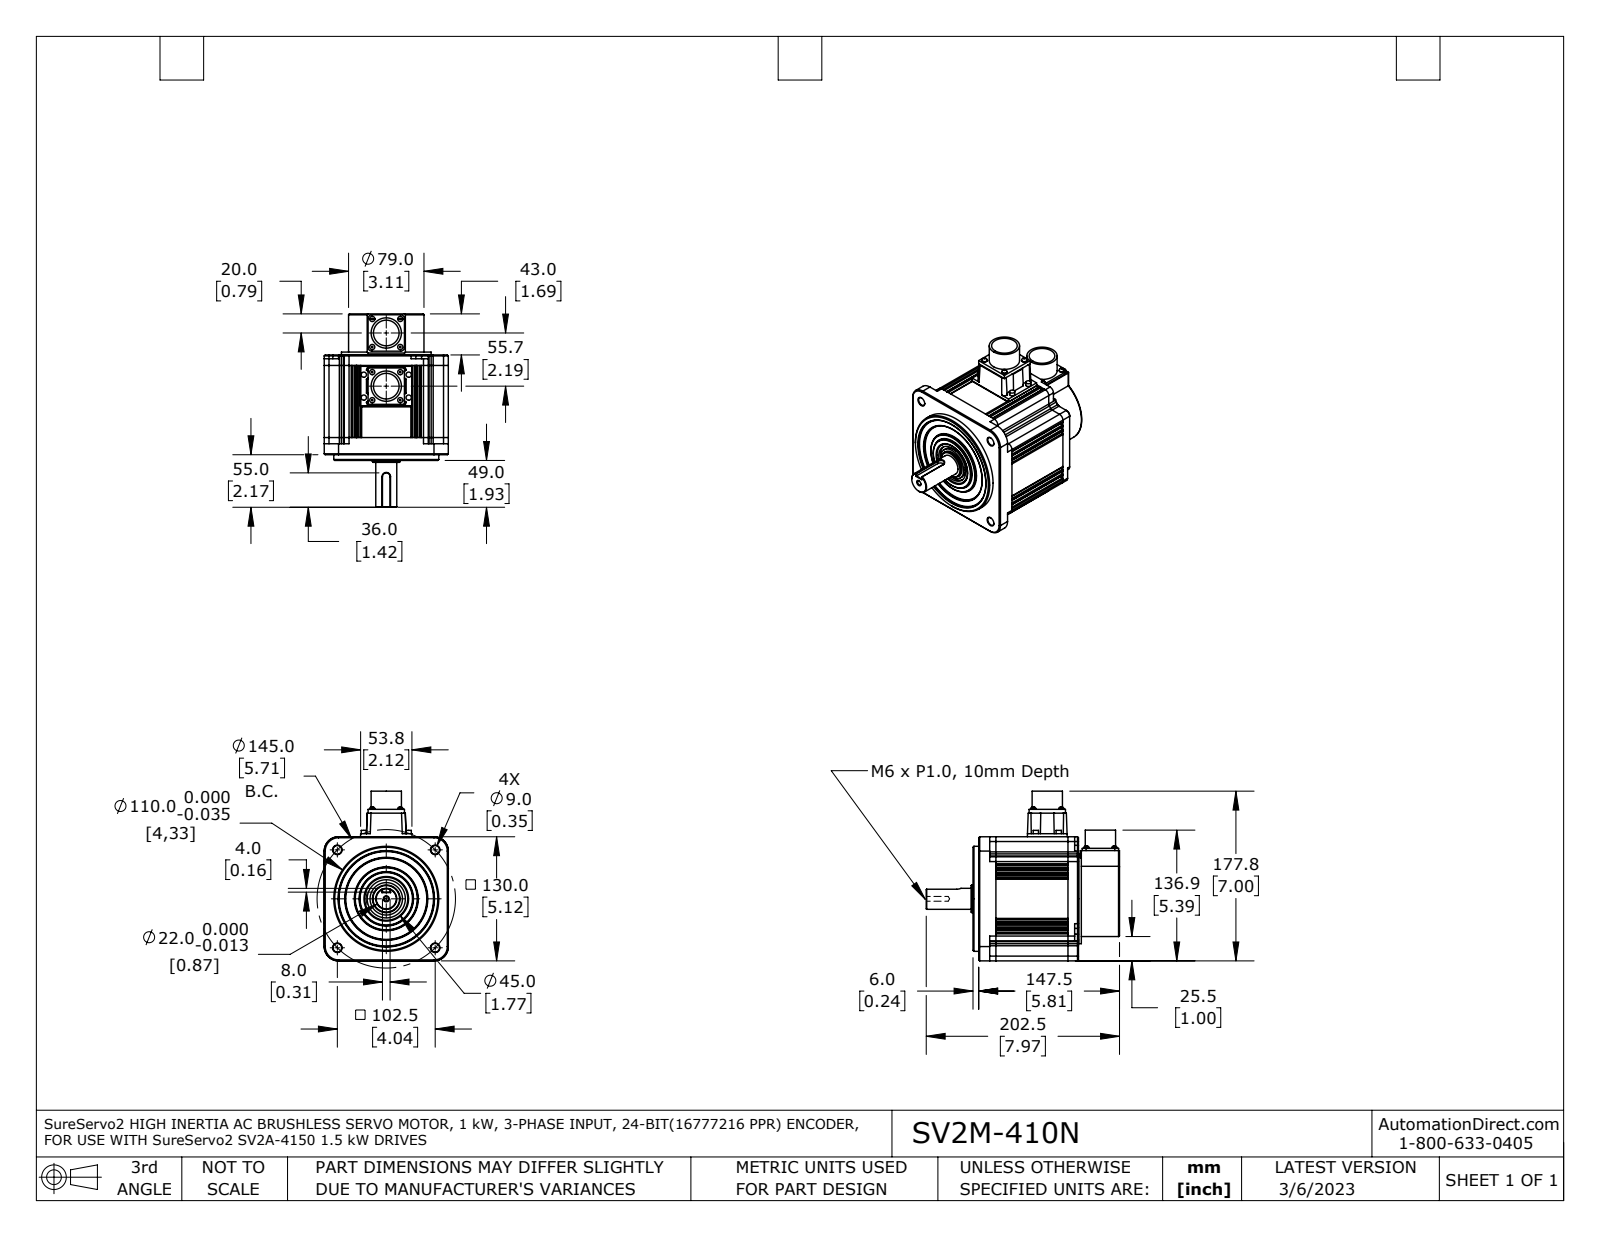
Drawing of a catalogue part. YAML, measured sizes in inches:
part_name: "SV2M-x10N fxt"
step_written_by: "SolidWorks 2021 (AUTOMOTIVE_DESIGN)"
units: inches
bodies: {solids: 2, faces: 593, planar: 281, cylindrical: 172, other: 140}
overall_size: [7.972, 6.998, 5.118]
volume: 117.7
surface_area: 208.6
round_holes:
  - {diameter: 0.354, count: 4}
  - {diameter: 1.058, count: 2}
  - {diameter: 0.197, count: 1}
  - {diameter: 1.142, count: 1}
  - {diameter: 1.575, count: 1}
  - {diameter: 1.772, count: 1}
  - {diameter: 3.386, count: 1}
  - {diameter: 3.937, count: 1}
round_bosses_or_shafts:
  - {diameter: 0.217, count: 6}
  - {diameter: 0.213, count: 6}
  - {diameter: 1.25, count: 2}
  - {diameter: 4.331, count: 1}
  - {diameter: 3.701, count: 1}
  - {diameter: 3.11, count: 1}
  - {diameter: 2.598, count: 1}
  - {diameter: 2.205, count: 1}
partial_cylinders:
  - {radius: 0.039, count: 70}
  - {radius: 0.157, count: 9}
  - {radius: 0.118, count: 8}
  - {radius: 0.197, count: 8}
face_to_face_distances: [4.291, 0.827, 4.114, 0.118, 5.118, 1.693, 5.807, 2.402, 0.059, 0.211]
hole_center_spacings: [2.855, 4.037, 5.709, 2.192]
